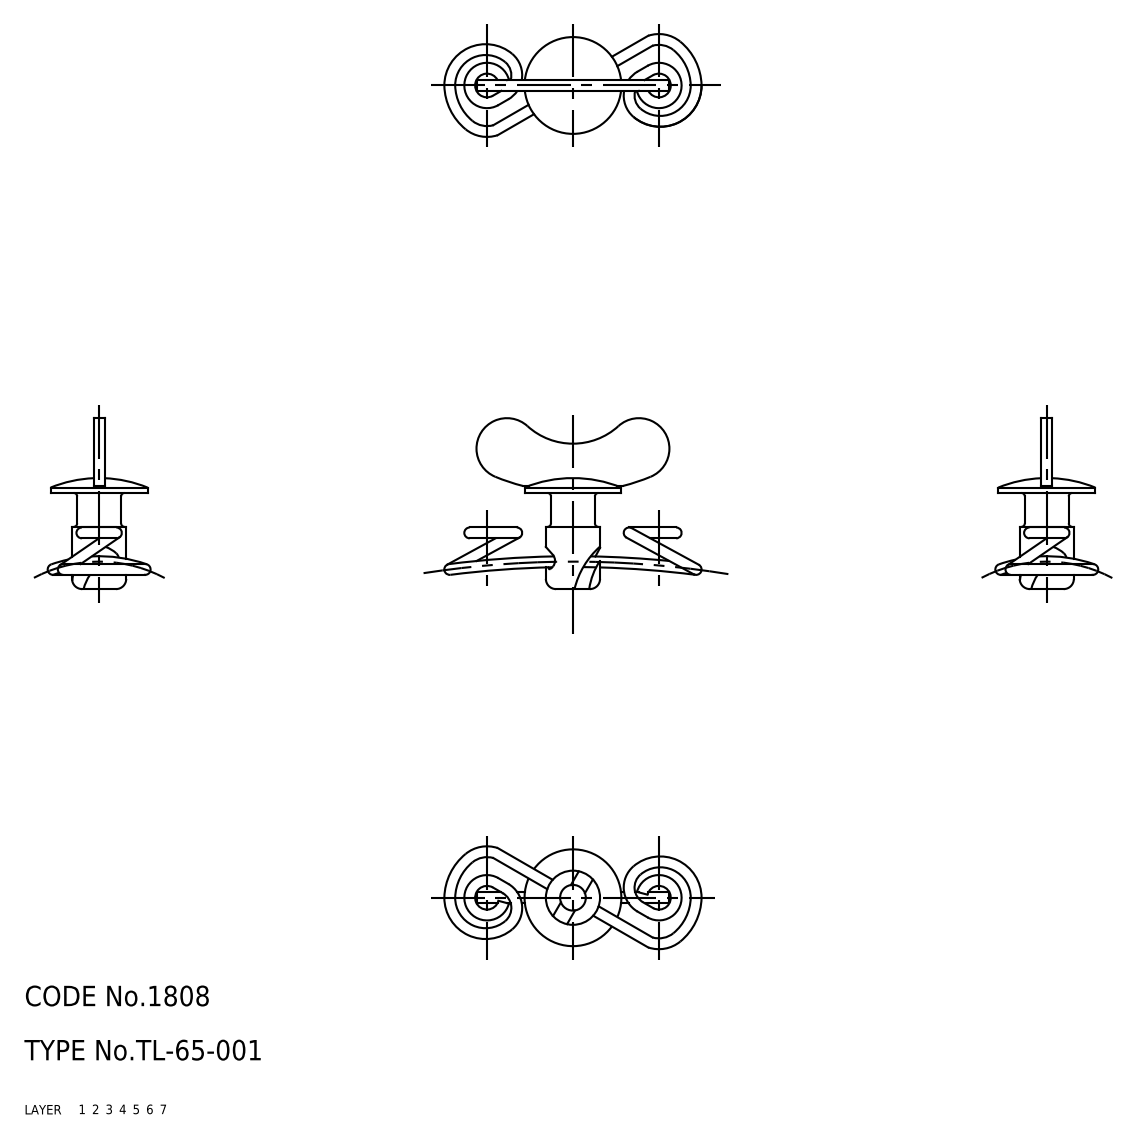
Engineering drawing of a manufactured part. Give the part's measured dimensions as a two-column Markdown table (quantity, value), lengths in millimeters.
| quantity | value |
| --- | --- |
| part name | fastener; spring; TL_65_001 |
| STEP written by | SolidWorks 2015 (AUTOMOTIVE_DESIGN) |
| units | millimeters |
| bodies | 2 solids, 82 faces (13 planar, 30 cylindrical, 39 other) |
| overall size | 38.01 × 25.25 × 15.07 |
| volume | 1 182 mm³ |
| surface area | 1 929 mm² |
| round holes (diameter × count) | 3.8 × 1 |
| round bosses / shafts (diameter × count) | 1.6 × 2, 14.3 × 1, 8 × 1, 6.5 × 1 |
| partial cylindrical surfaces (radius × count) | 1.2 × 2, 2.94 × 2, 4.5 × 2, 5.34 × 2, 10 × 1, 30 × 1 |
| main face-to-face distances | 1.6, 5, 9.2, 14.2, 15.25, 6.05, 1.05, 6.58 |
